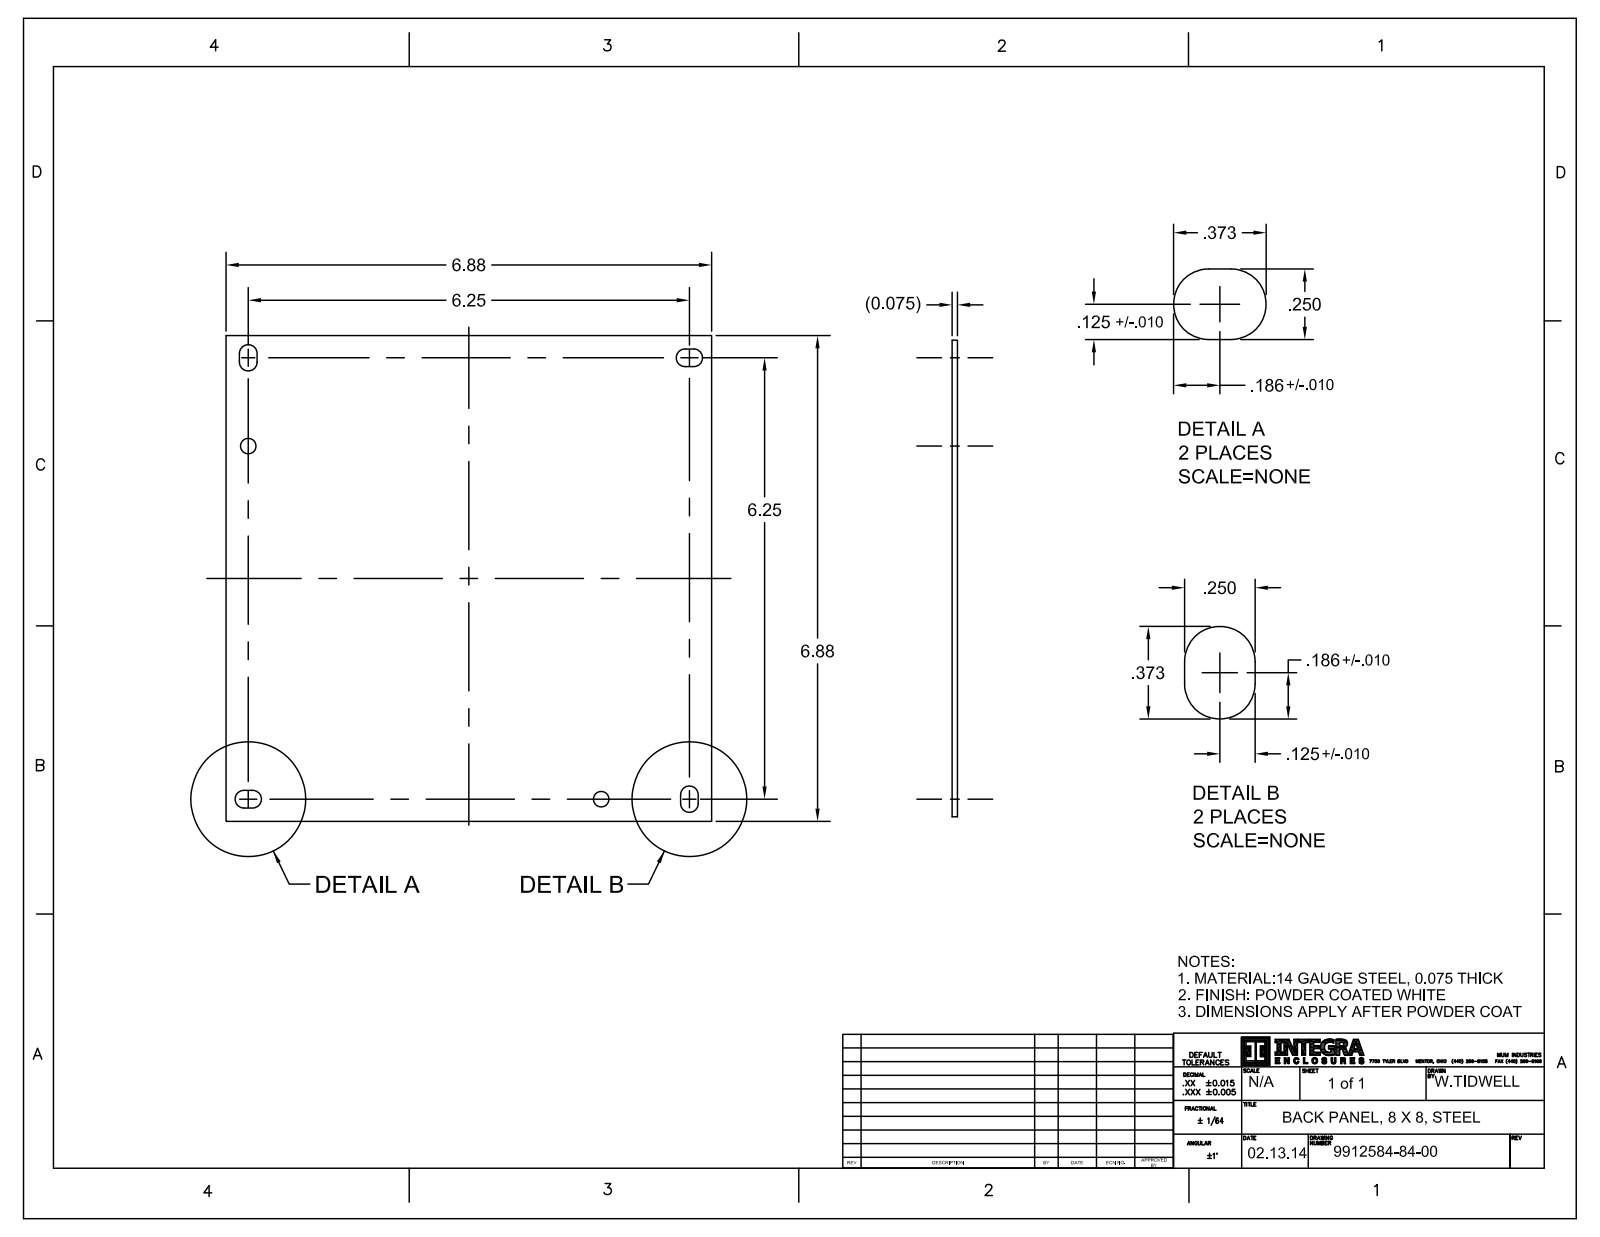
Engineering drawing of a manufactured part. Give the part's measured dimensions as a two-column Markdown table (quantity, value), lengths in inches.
| quantity | value |
| --- | --- |
| part name | 9912584-84-00; 9912518-82-10; SBP88_ASM |
| STEP written by | CREO PARAMETRIC BY PTC INC, 2016050 (CONFIG_CONTROL_DESIGN) |
| units | inches |
| bodies | 5 solids, 434 faces (90 planar, 272 cylindrical, 72 other) |
| overall size | 6.88 × 6.88 × 0.443 |
| volume | 3.574 in³ |
| surface area | 98.87 in² |
| round holes (diameter × count) | 0.219 × 2 |
| round bosses / shafts (diameter × count) | 0.373 × 4, 0.19 × 4, 0.149 × 4 |
| partial cylindrical surfaces (radius × count) | 0.004 × 48, 0.125 × 8 |
| main face-to-face distances | 0.075, 6.88, 0.238, 0.313, 6.225, 2.381, 5.75, 0.19, 0.44, 6.44 |
| hole center spacings | 7.071 |
